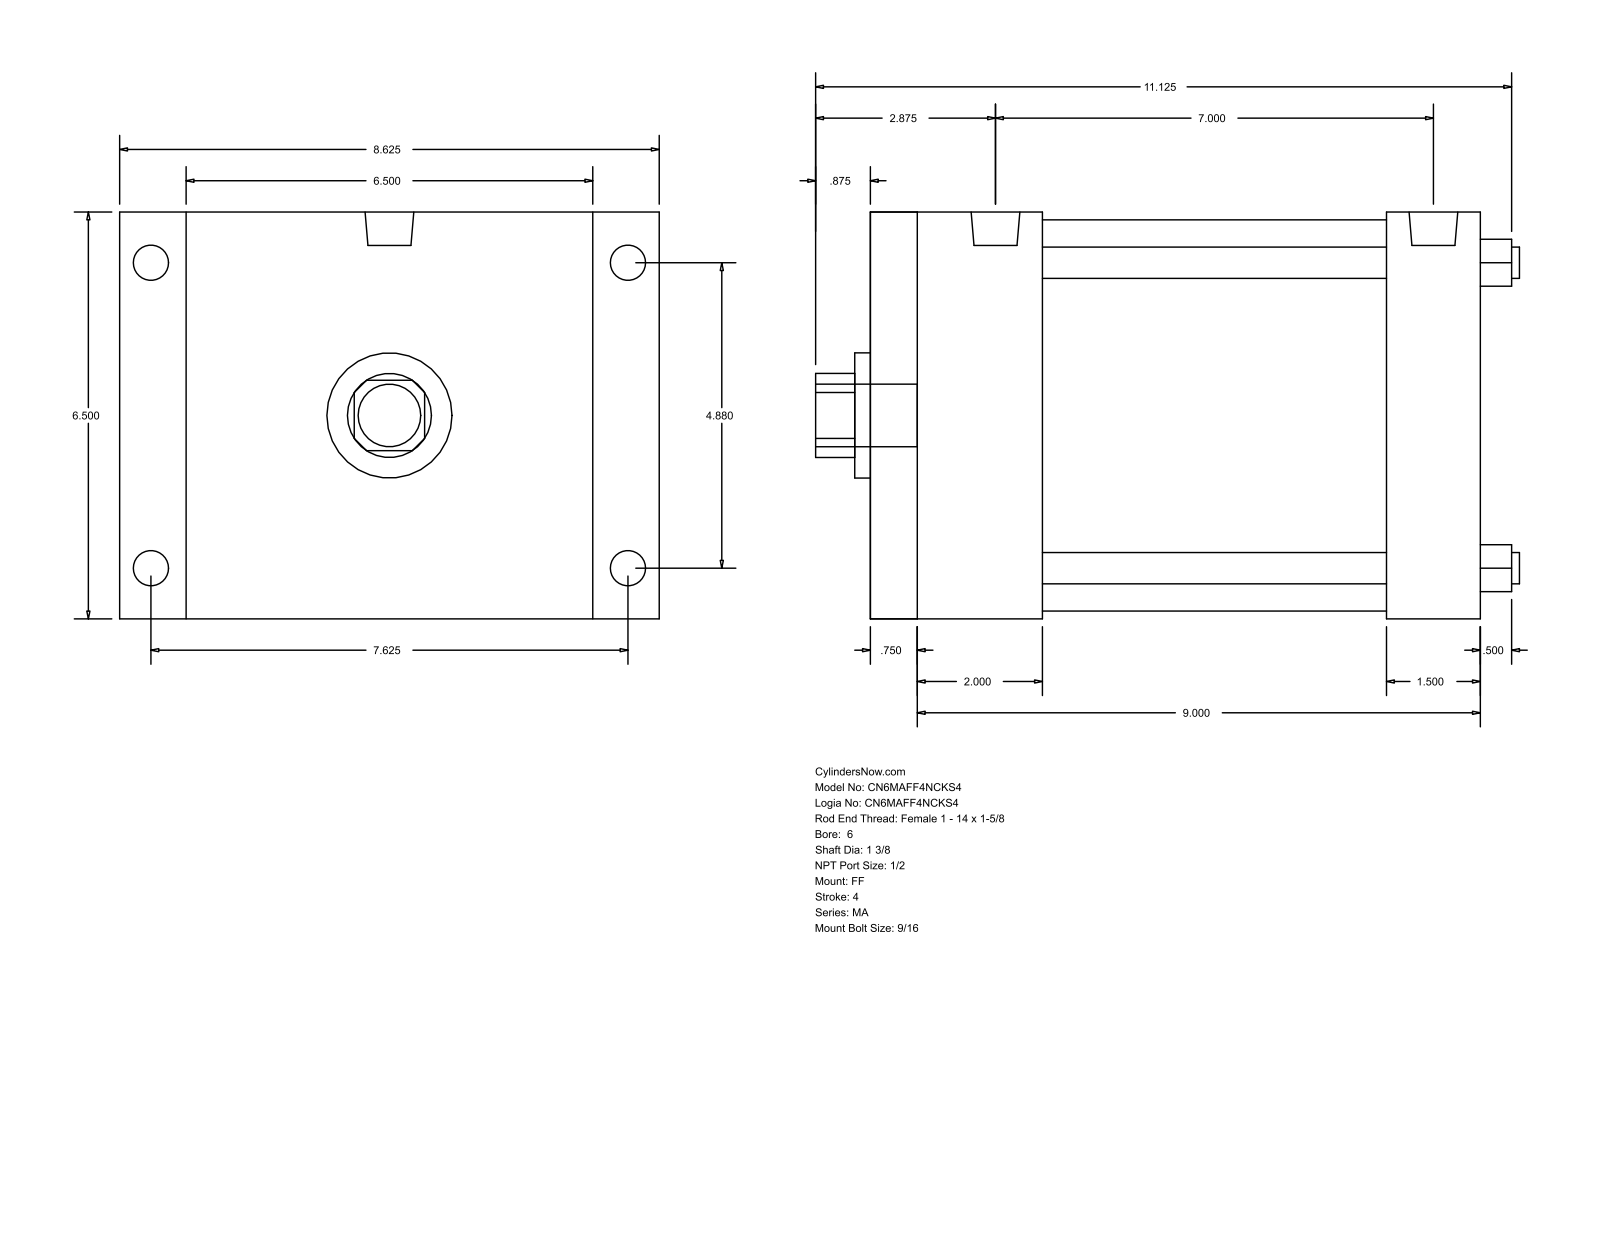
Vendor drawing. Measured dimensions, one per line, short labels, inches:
name: MA_FF__0600_1.375
written by: GSSL Pune (CONFIG_CONTROL_DESIGN)
unit: in
bodies: 0 solids, 92 faces (64 planar, 28 cylindrical, 0 other)
size: 11.25 × 8.625 × 6.5
holes: 4× ⌀0.5, 1× ⌀1.375, 1× ⌀2, 1× ⌀6.25
bosses: 4× ⌀0.687, 4× ⌀0.563, 2× ⌀0.778, 1× ⌀1
rounds: 1× R0.672
face distances: 6.5, 9.75, 0.625, 9.125, 1.5, 2.625, 2, 7.125, 8.25, 7.625
hole spacings: 3.451, 4.88, 6.902
